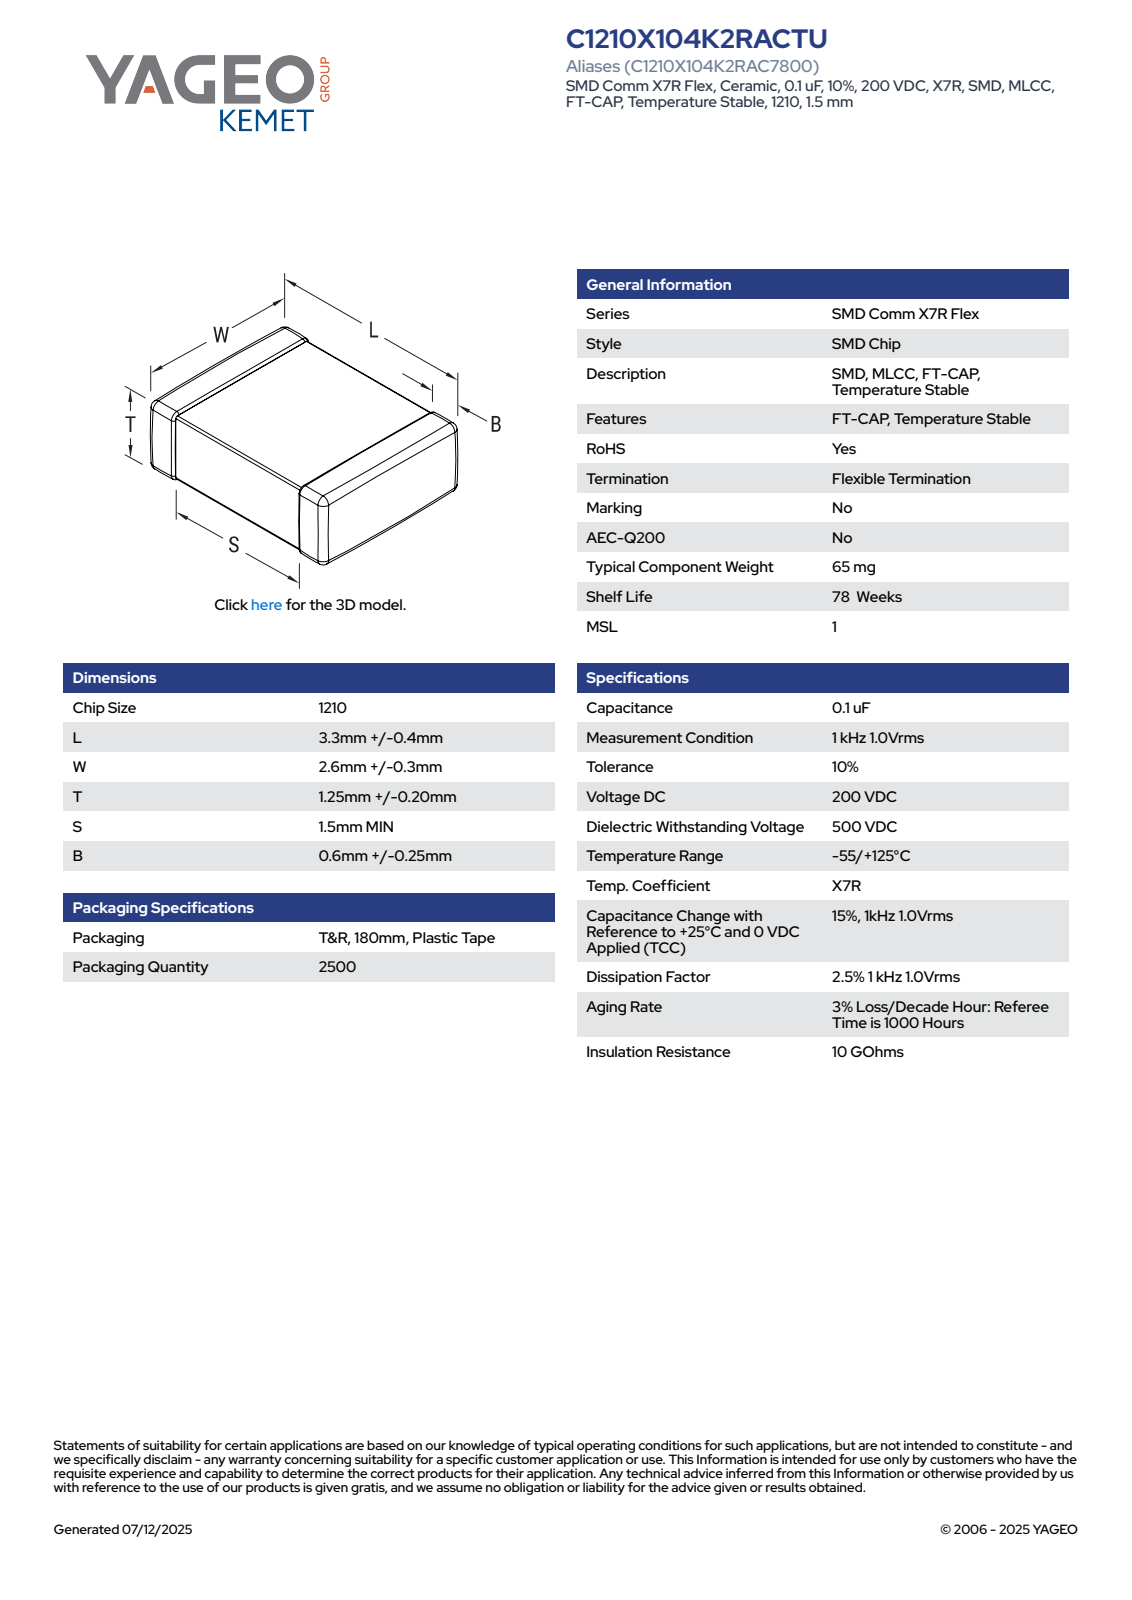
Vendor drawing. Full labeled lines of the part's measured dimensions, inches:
Part name (STEP PRODUCT): CCS_CCSTDNOS_1210_L3.7W2.9T1.45B0.85
STEP written by: SolidWorks 2014 (AUTOMOTIVE_DESIGN)
Units: inches
Bodies: 4 solids, 125 faces (71 planar, 38 cylindrical, 16 other)
Overall size (bounding box): 0.146 × 0.114 × 0.057
Volume: 0.001 in³ · Surface area: 0.062 in²
Main face-to-face distances: 0.055, 0.052, 0.057, 0.112, 0.146, 0.109, 0.114, 0.055, 0.059, 0.053
